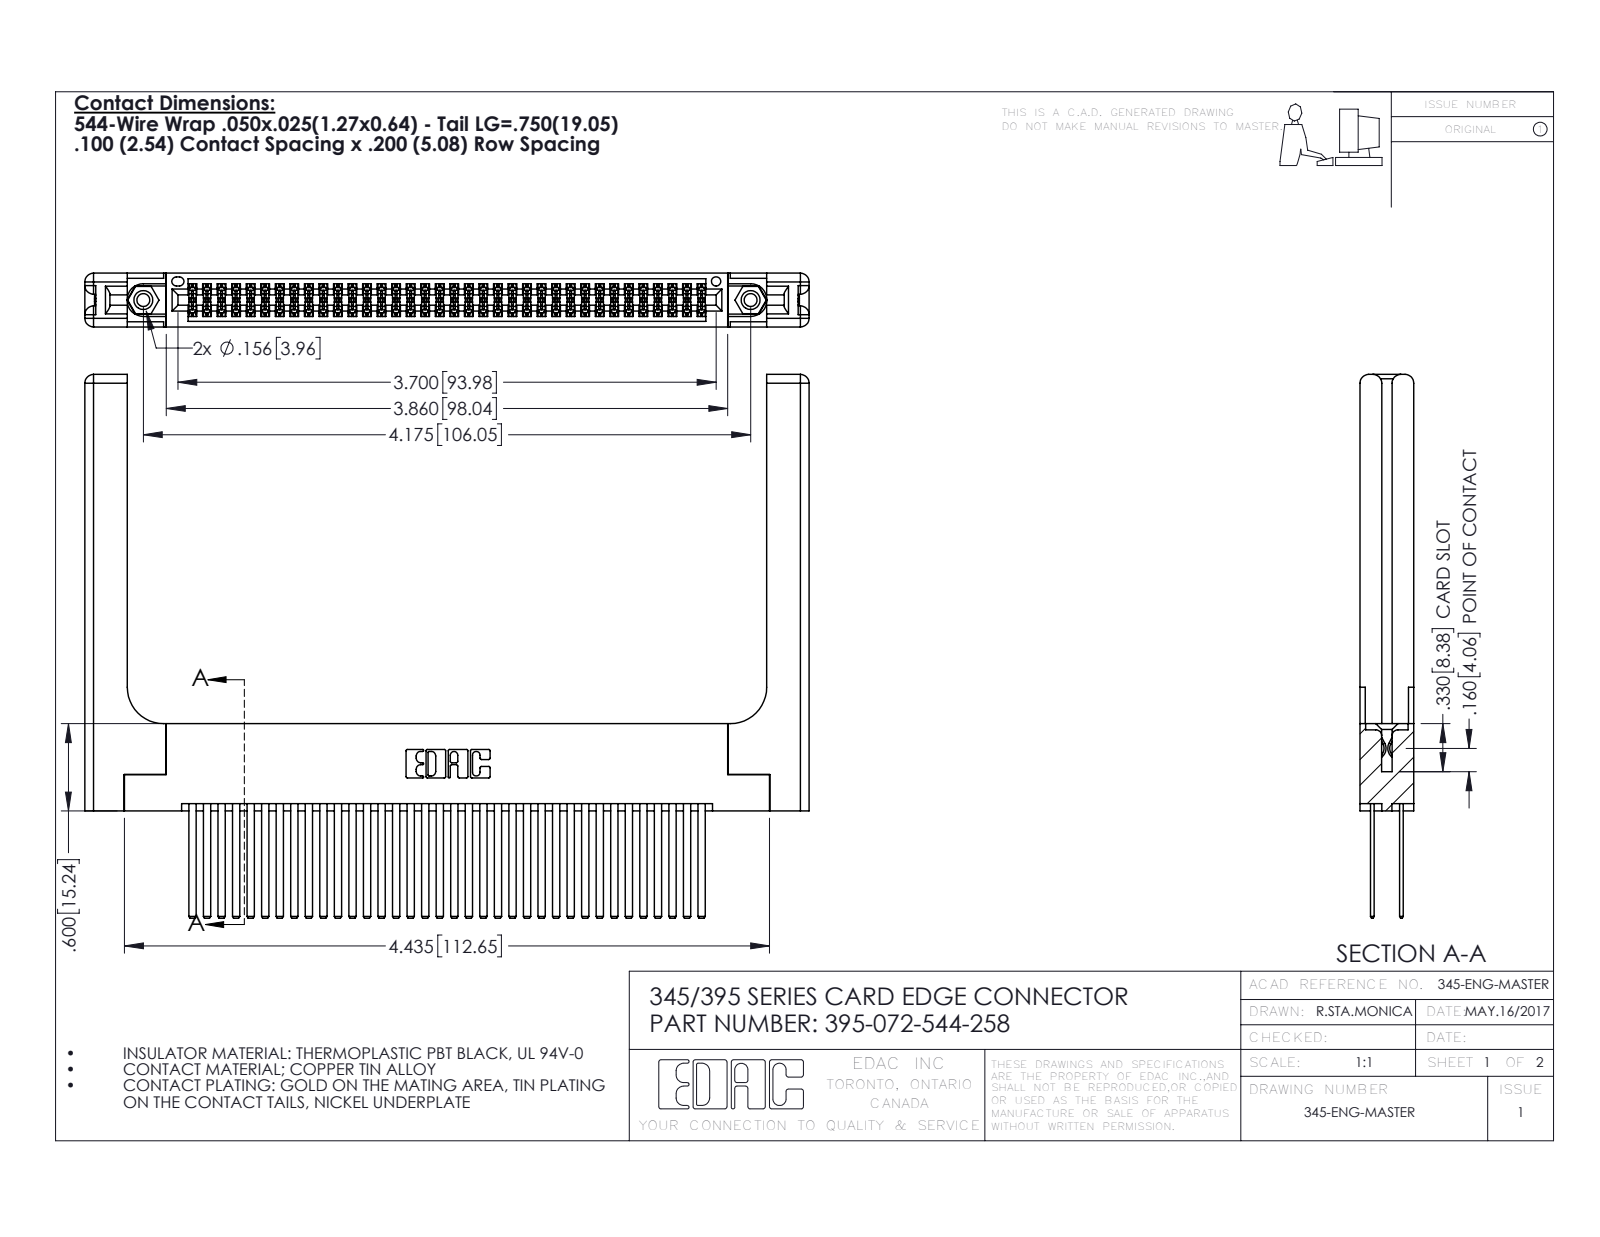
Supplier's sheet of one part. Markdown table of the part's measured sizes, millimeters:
| quantity | value |
| --- | --- |
| part name | 345-292-001_345-293-144; 345-220-058_345-220-058; 345-250-001_345-250-001-102; 345 Part_Flush Mounting Lugs - 0.156 Dia-TH (+1 more) |
| STEP written by | SolidWorks 2016 (CONFIG_CONTROL_DESIGN) |
| units | millimeters |
| bodies | 77 solids, 3550 faces (2316 planar, 1174 cylindrical, 60 other) |
| overall size | 126.5 × 94.9 × 9.4 |
| volume | 21 710 mm³ |
| surface area | 27 470 mm² |
| round holes (diameter × count) | 2.3 × 2, 3.2 × 2, 4 × 2, 1.6 × 1 |
| round bosses / shafts (diameter × count) | 3.9 × 2 |
| partial cylindrical surfaces (radius × count) | 0.2 × 108, 0.3 × 22, 1.5 × 16, 0.2 × 6, 0.8 × 6, 0.7 × 3, 0.4 × 2, 0.5 × 2 |
| main face-to-face distances | 1.8, 7.6, 5.1, 2.5, 6.9, 0.6, 9.4, 5.7, 4.4, 3.8 |
| hole center spacings | 6.9, 100.1, 106 |
